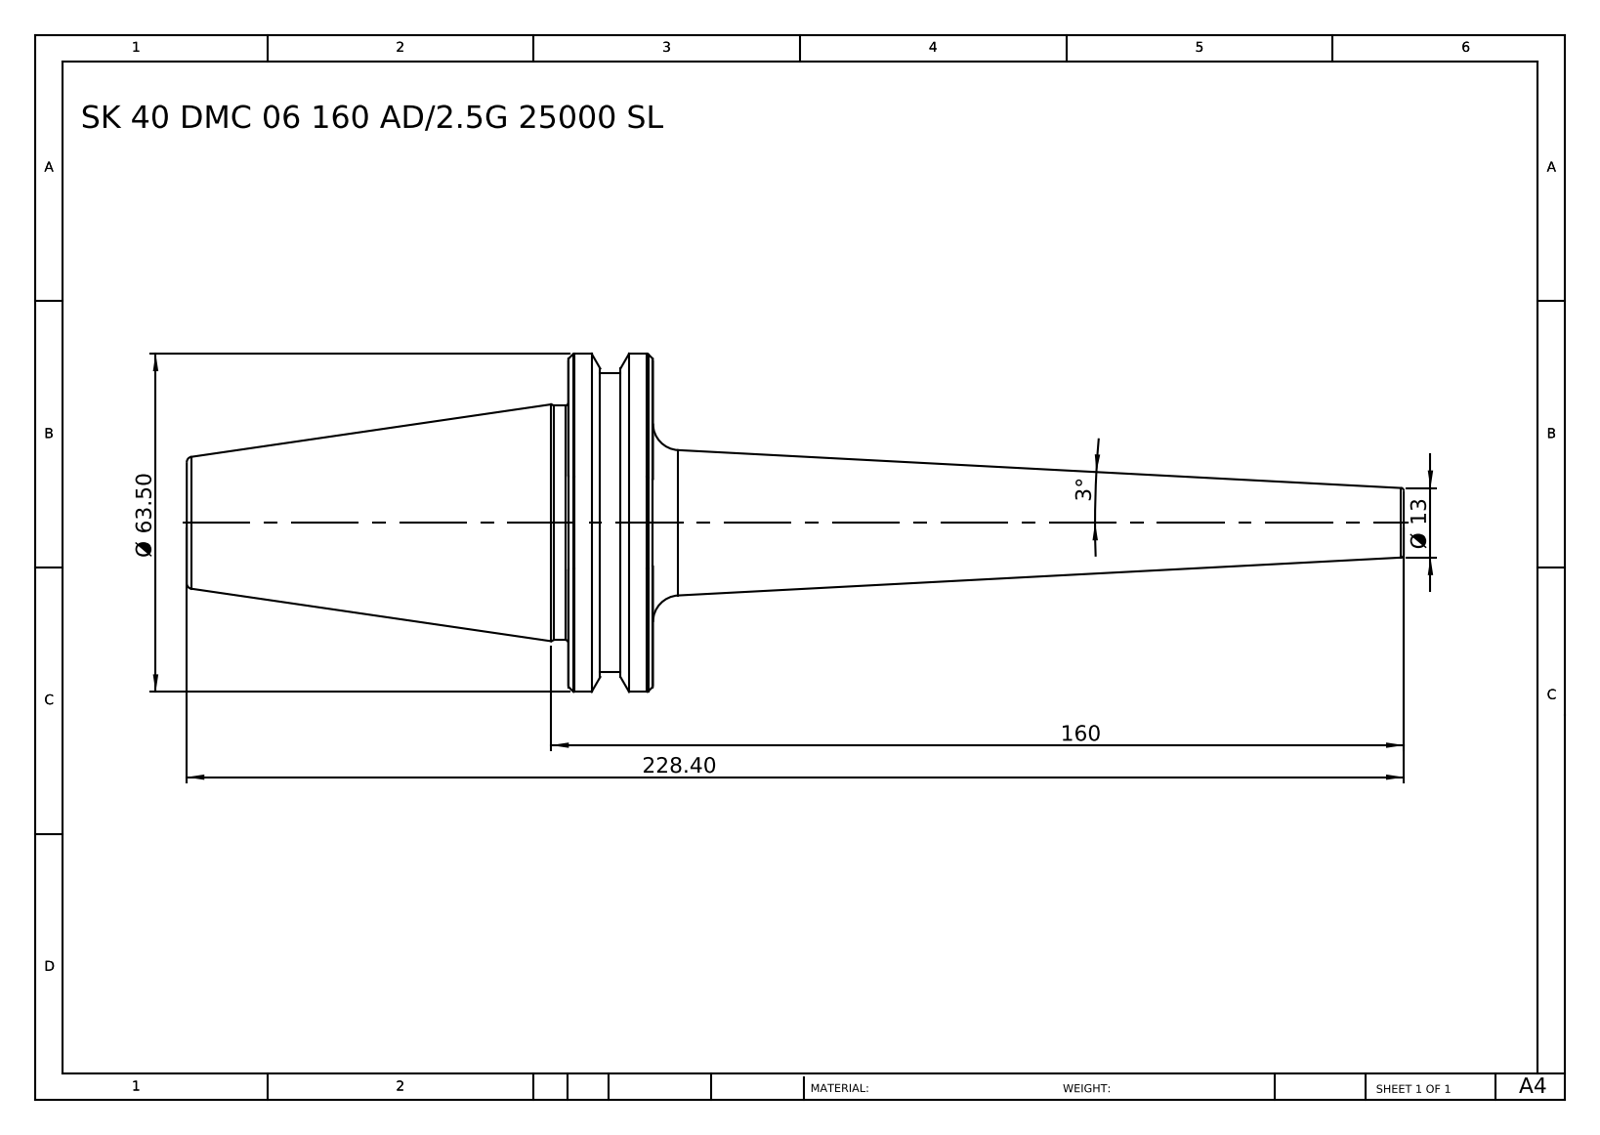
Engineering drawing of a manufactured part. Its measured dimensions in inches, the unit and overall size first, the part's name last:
Units: inches
Overall size (bounding box): 8.992 × 2.5 × 2.5
Round bosses / shafts (diameter × count): ⌀2.5 ×1, ⌀2.205 ×1, ⌀1.732 ×1
Main face-to-face distances: 0.626, 3.445, 2.819, 0.39, 0.236, 3.055, 0.24, 0.15, 0.386, 3.205
Volume: 10.1 in³ · Surface area: 39.26 in²
Bodies: 1 solid, 64 faces (6 planar, 8 cylindrical, 50 other)
Part name (STEP PRODUCT): SK 40 DMC 06 160 AD-2.5G 25000 SL
STEP written by: SolidWorks 2014 (CONFIG_CONTROL_DESIGN)
